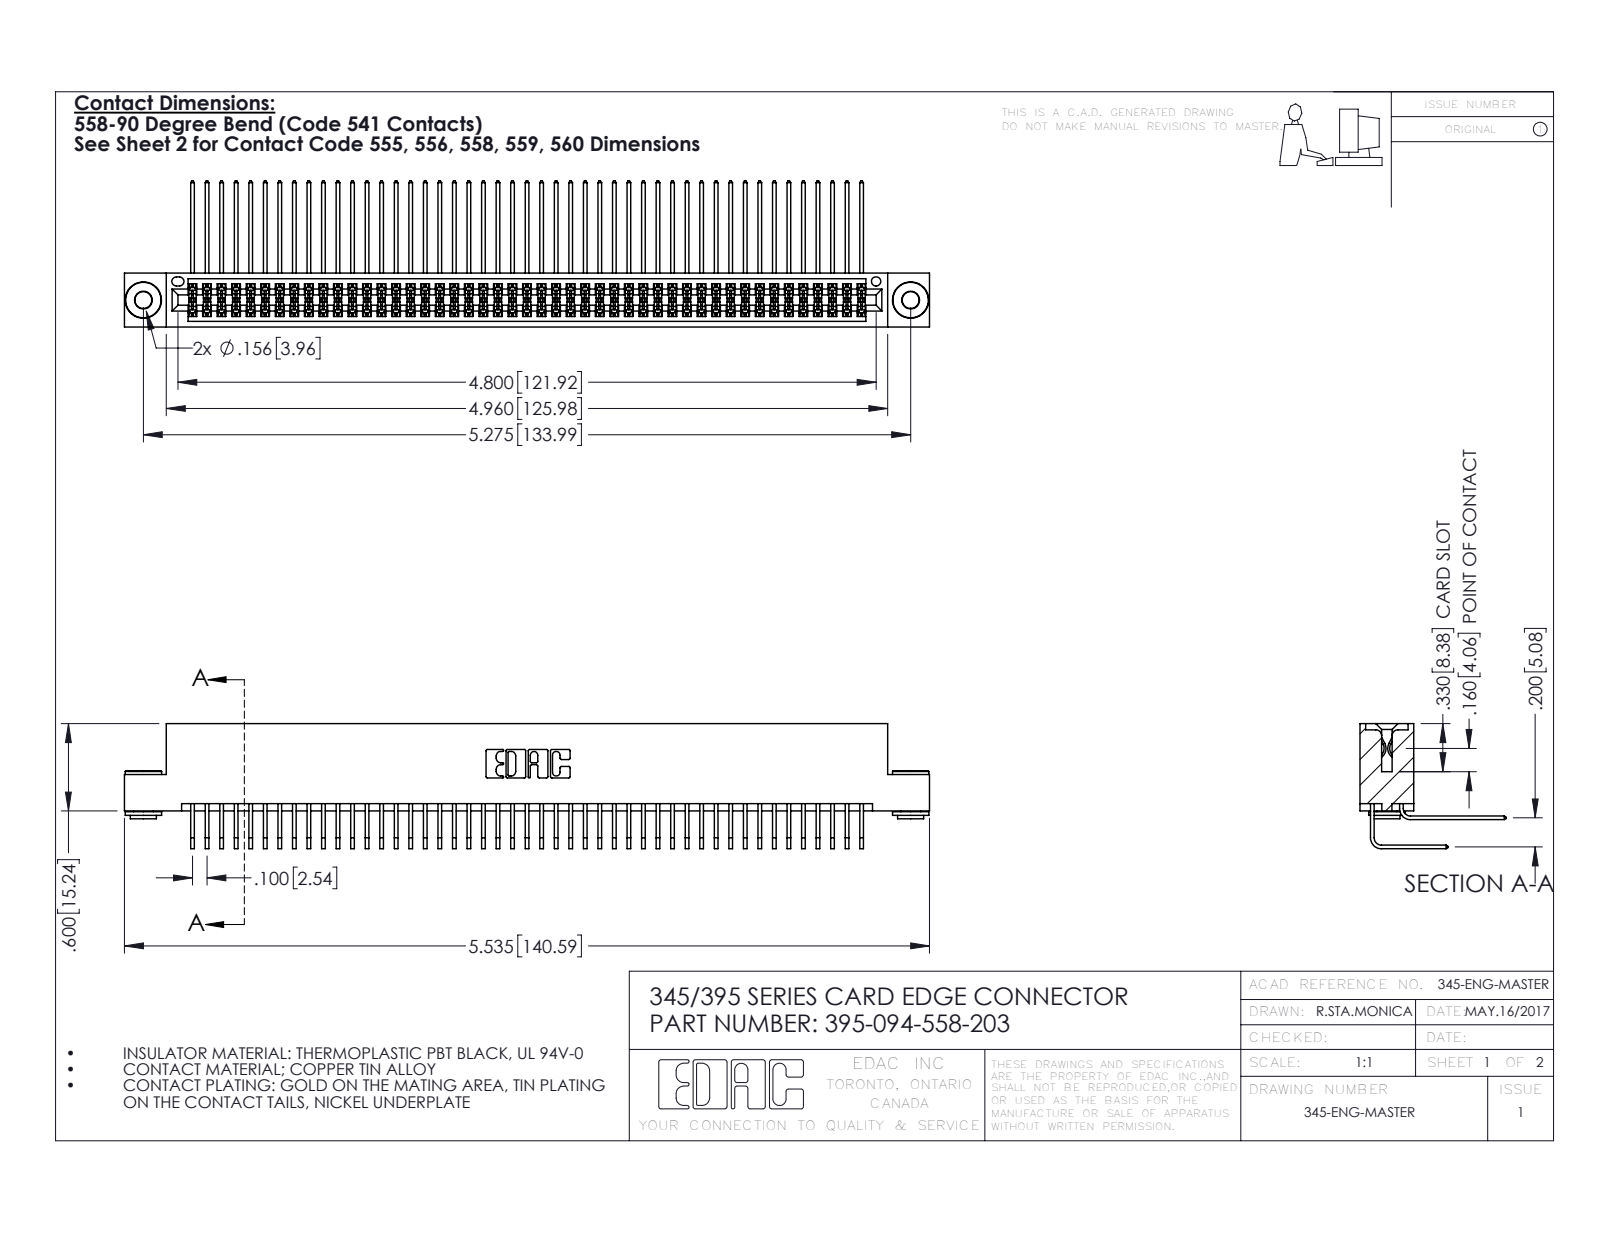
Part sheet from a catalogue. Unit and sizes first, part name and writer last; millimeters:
Units: millimetres
Overall size (bounding box): 140.6 × 25.5 × 21.8
Round holes (diameter × count): ⌀2.9 ×2, ⌀4 ×2, ⌀1.6 ×1
Round bosses / shafts (diameter × count): ⌀6.4 ×2, ⌀4.6 ×2, ⌀3.5 ×2
Partial cylindrical surfaces — rounded edges, fillets, slot ends (radius × count): R0.2 ×142, R0.3 ×22, R0.2 ×6, R0.8 ×6, R0.7 ×3, R0.4 ×2, R0.5 ×2, R0.6 ×2
Main face-to-face distances: 1.8, 7.6, 5.1, 9.4, 0.6, 2.5, 6.9, 5.7, 0.6, 4.4
Hole centre spacings: 6.9, 128, 134
Volume: 14 300 mm³ · Surface area: 23 940 mm²
Bodies: 97 solids, 5052 faces (3380 planar, 1664 cylindrical, 8 other)
Part name (STEP PRODUCT): 345-292-001_558 Tail - 2; 345 Part_Flush Mounting Lugs - 0.156 Dia-TH; 345-292-001_558 559 Tail - 1; 345-250-002_345-250-002-102 (+1 more)
STEP written by: SolidWorks 2016 (CONFIG_CONTROL_DESIGN)
